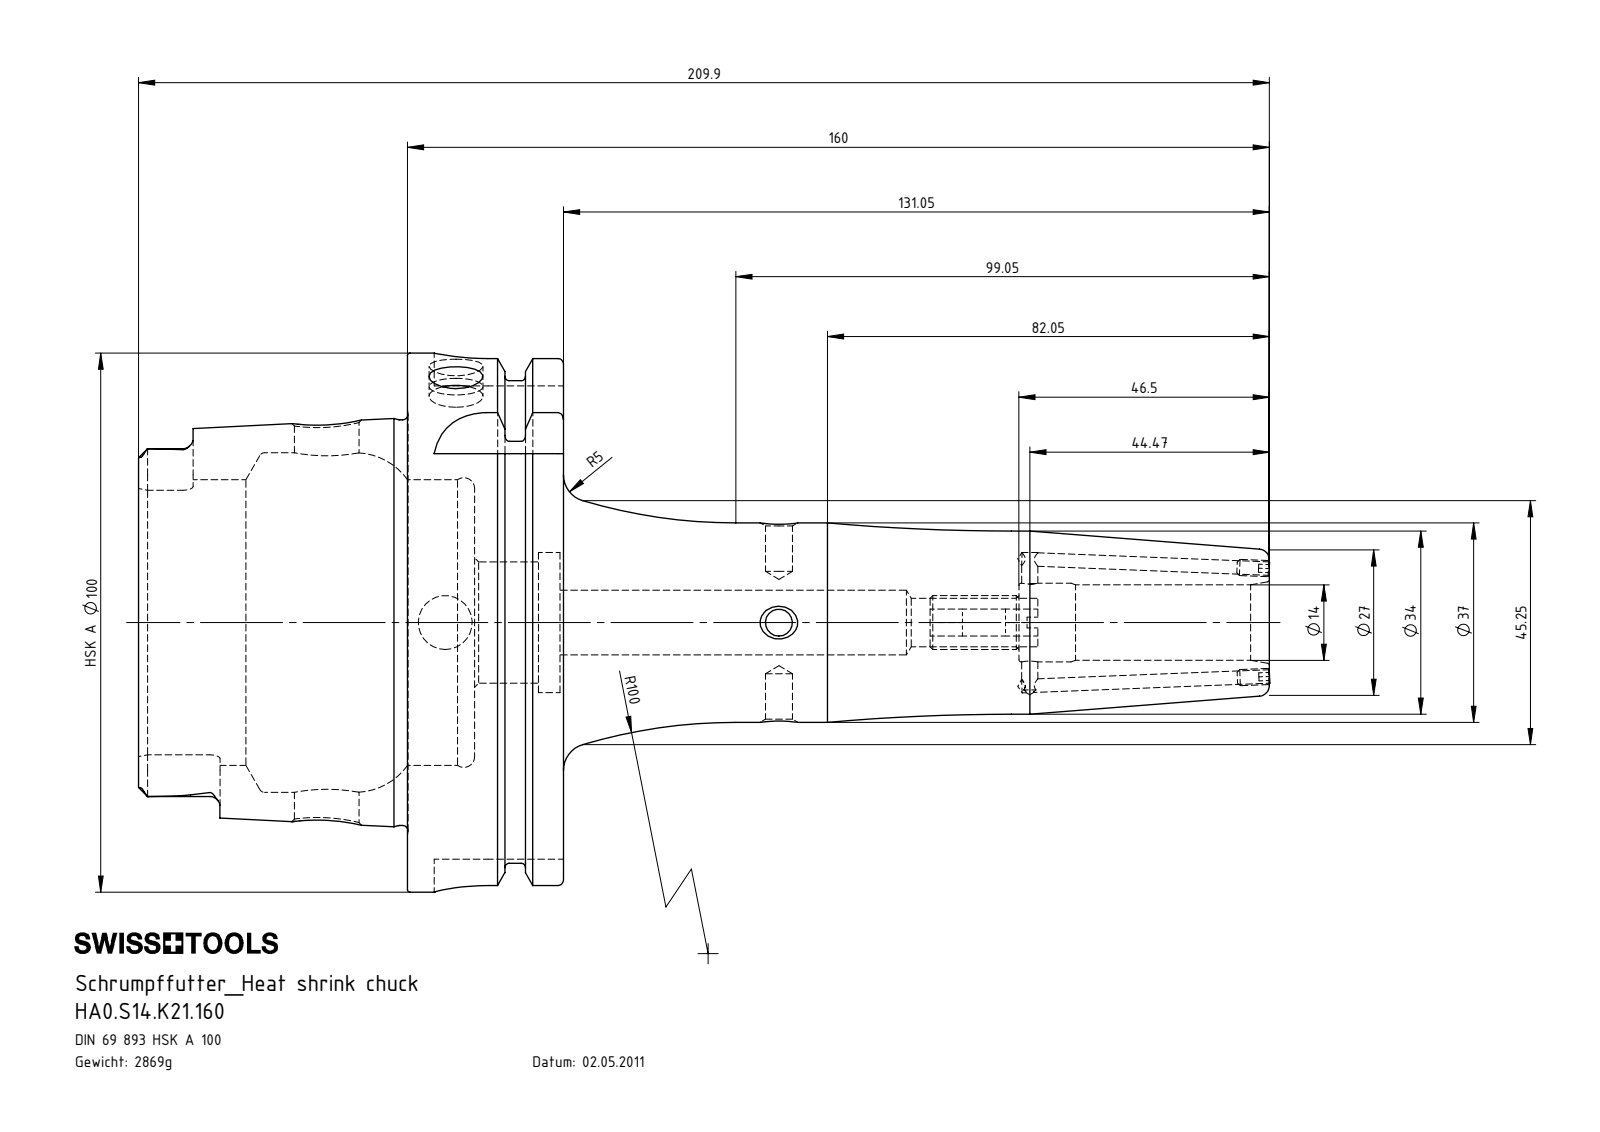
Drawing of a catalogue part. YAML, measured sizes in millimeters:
part_name: "HA0-S14.K21.160; ERU-CJ2.001.006; ERU-AN4.K01.020_A; HA0-S14.K21.160_C_Fertigbearbeitung"
step_written_by: "SolidWorks 2012 (CONFIG_CONTROL_DESIGN)"
units: millimeters
bodies: {solids: 4, faces: 300, planar: 95, cylindrical: 88, other: 117}
overall_size: [209.98, 100, 100]
volume: 365426
surface_area: 70425
round_holes:
  - {diameter: 5, count: 3}
  - {diameter: 10, count: 3}
  - {diameter: 2.5, count: 2}
  - {diameter: 12, count: 2}
  - {diameter: 3, count: 1}
  - {diameter: 9, count: 1}
  - {diameter: 14, count: 1}
  - {diameter: 14.6, count: 1}
  - {diameter: 22.5, count: 1}
  - {diameter: 26, count: 1}
  - {diameter: 53, count: 1}
  - {diameter: 63, count: 1}
round_bosses_or_shafts:
  - {diameter: 3, count: 2}
  - {diameter: 100, count: 1}
  - {diameter: 91.95, count: 1}
  - {diameter: 75.26, count: 1}
  - {diameter: 37, count: 1}
  - {diameter: 34, count: 1}
  - {diameter: 10, count: 1}
partial_cylinders:
  - {radius: 1.9, count: 6}
  - {radius: 4.88, count: 4}
  - {radius: 10, count: 4}
face_to_face_distances: [28.95, 16.5, 12.45, 49.9, 62.35, 78.85, 87.8, 78.2, 28.3, 15.85]
hole_center_spacings: [46.55, 61.95, 83.95, 130.5]
